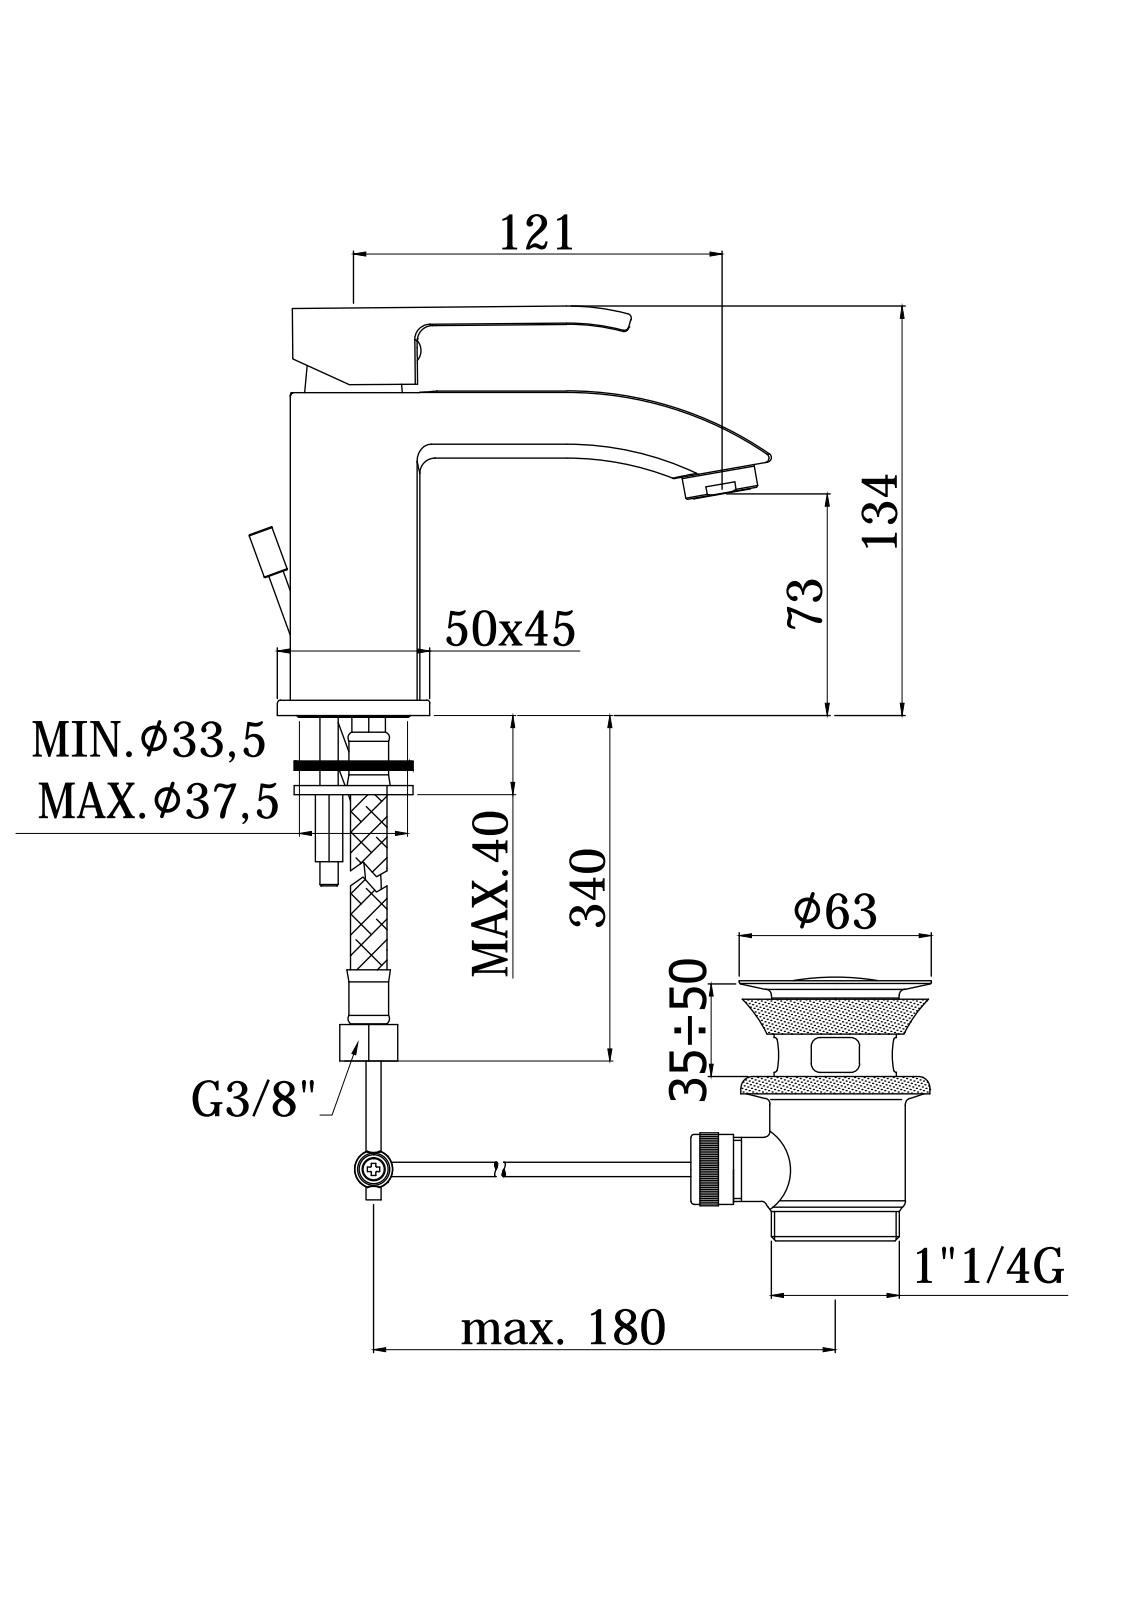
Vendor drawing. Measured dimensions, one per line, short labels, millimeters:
name: LES075CR
written by: CREO PARAMETRIC BY PTC INC, 2020044 (CONFIG_CONTROL_DESIGN)
unit: mm
bodies: 5 solids, 2721 faces (1762 planar, 509 cylindrical, 450 other)
size: 172.19 × 135.03 × 45
volume: 167 850 mm³; area: 94 976 mm²
holes: 3× ⌀5, 2× ⌀3.5, 2× ⌀4.6, 2× ⌀5.25, 2× ⌀6.2, 2× ⌀9, 2× ⌀11, 1× ⌀3, 1× ⌀5.5, 1× ⌀7.8, 1× ⌀16, 1× ⌀16.7
bosses: 3× ⌀5, 2× ⌀10.8, 2× ⌀10, 2× ⌀8.2, 2× ⌀6, 2× ⌀4, 2× ⌀3, 1× ⌀38.8
rounds: 78× R0.5, 53× R1, 16× R2, 12× R0.3, 10× R0.7, 9× R1.5, 8× R0.25, 8× R3
face distances: 3, 33.5, 36.5, 30.5, 0.75, 2.25, 32.75, 35.75, 5, 1
hole spacings: 9.01, 2.76, 5, 6.72, 8.94, 9.33, 12.25, 13.46
